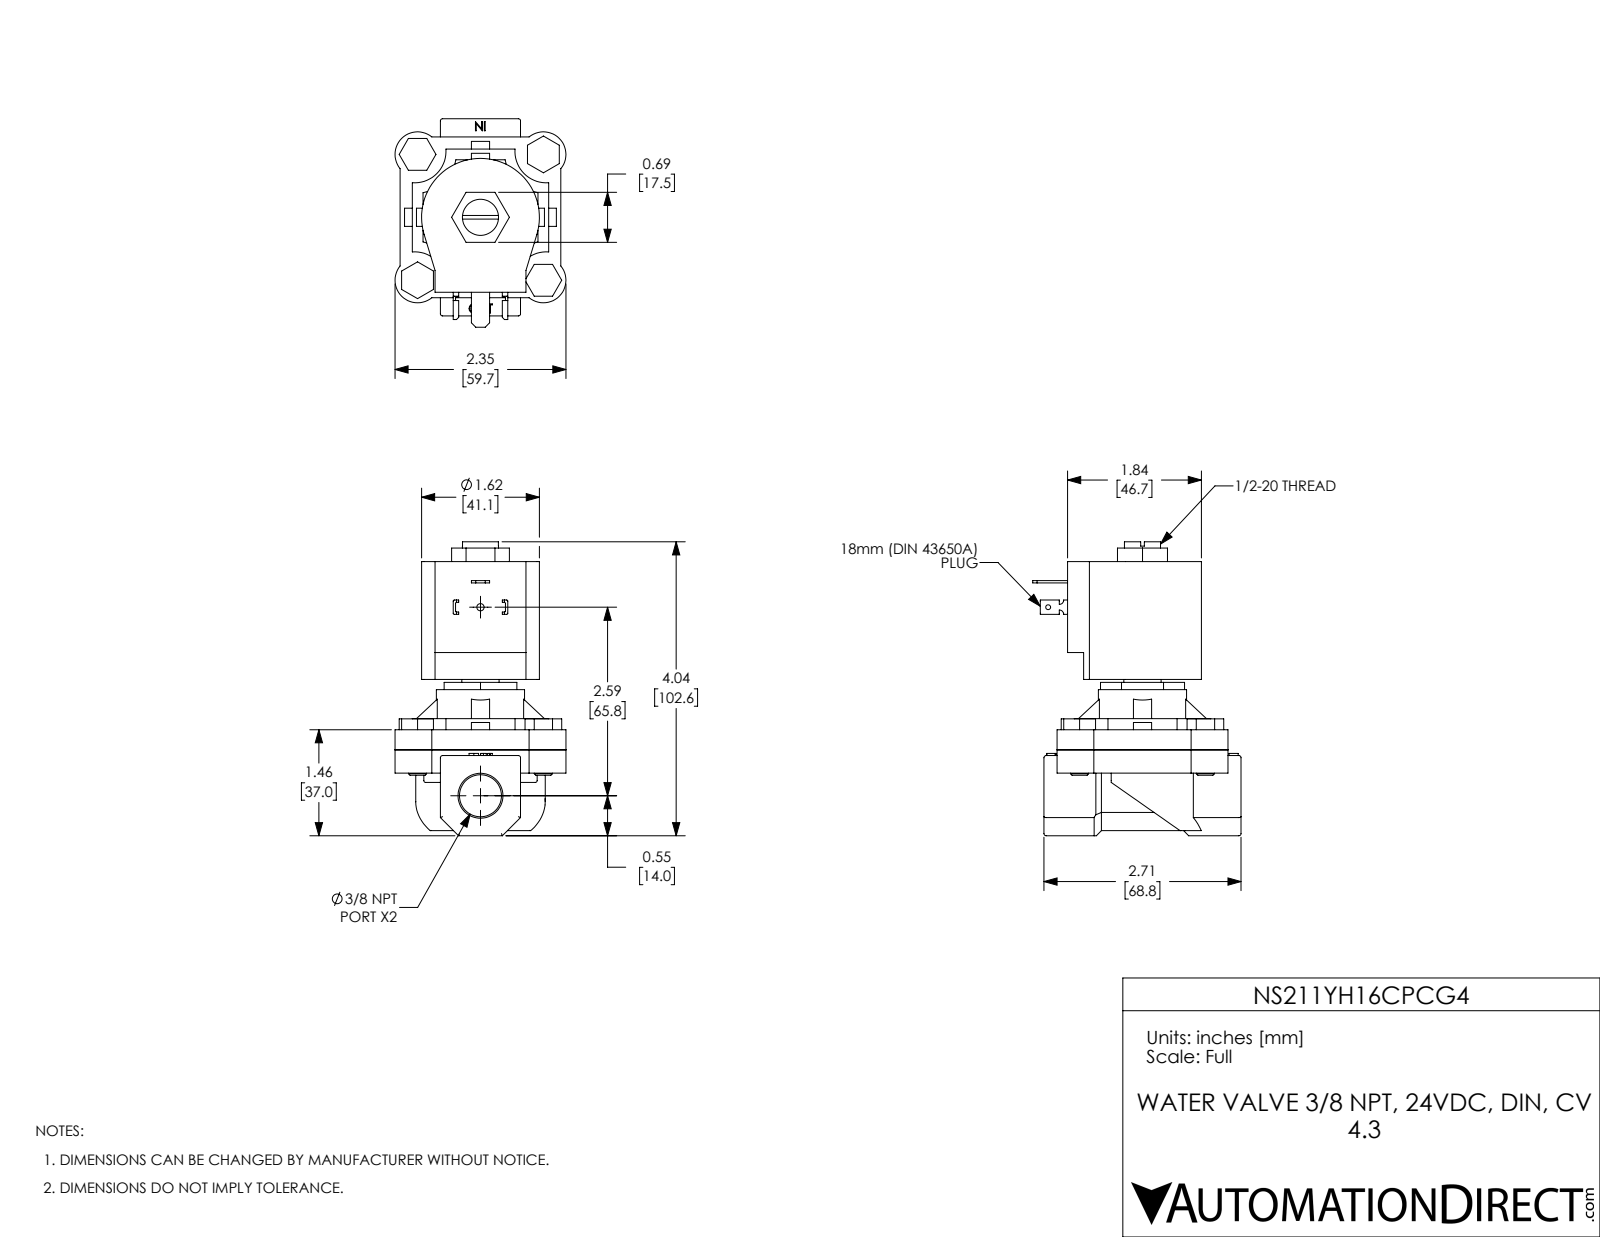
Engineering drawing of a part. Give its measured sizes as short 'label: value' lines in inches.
name: NS211YH16CPCG4
written by: SolidWorks 2024 (CONFIG_CONTROL_DESIGN)
unit: in
bodies: 11 solids, 383 faces (237 planar, 113 cylindrical, 33 other)
size: 4.04 × 2.865 × 2.35
volume: 10.3 in³; area: 66.77 in²
holes: 4× ⌀0.25, 1× ⌀0.067, 1× ⌀0.1, 1× ⌀0.496, 1× ⌀0.512, 1× ⌀0.578, 1× ⌀1.155
bosses: 4× ⌀0.248, 1× ⌀1.213
rounds: 15× R0.03, 8× R0.015, 4× R0.31, 4× R0.432, 4× R0.579, 2× R0.06, 1× R0.81, 1× R0.89
face distances: 0.276, 2.587, 2.311, 0.32, 0.596, 2.907, 0.554, 1.656, 0.25, 2.21
hole spacings: 1.223, 1.73, 2.446, 2.591
